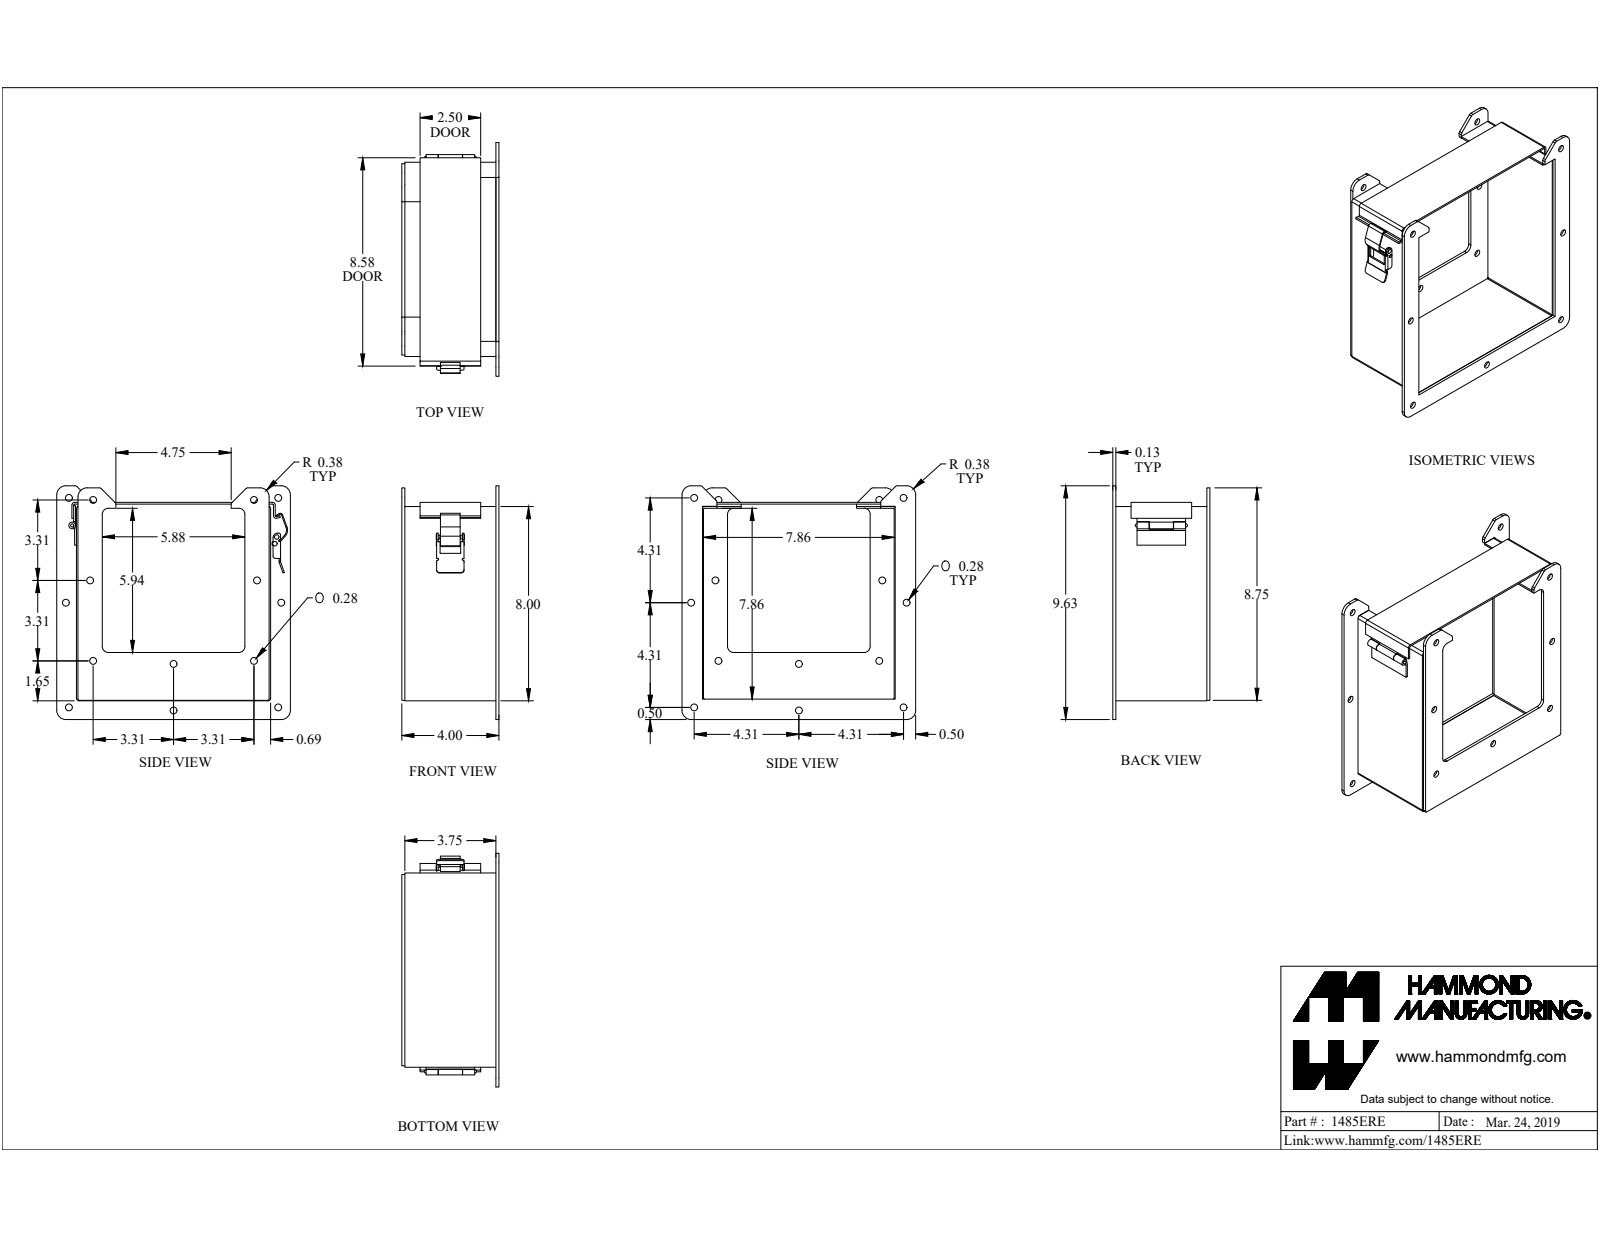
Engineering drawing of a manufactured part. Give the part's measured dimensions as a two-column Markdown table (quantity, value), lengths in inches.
| quantity | value |
| --- | --- |
| part name | 1485ERE |
| STEP written by | SolidWorks 2019 (CONFIG_CONTROL_DESIGN) |
| units | inches |
| bodies | 10 solids, 255 faces (146 planar, 107 cylindrical, 2 other) |
| overall size | 9.625 × 9.625 × 4 |
| volume | 15.79 in³ |
| surface area | 387 in² |
| round holes (diameter × count) | 0.281 × 14, 0.125 × 1, 0.13 × 1, 0.164 × 1 |
| round bosses / shafts (diameter × count) | 0.187 × 2, 0.275 × 1, 0.156 × 1, 0.125 × 1 |
| partial cylindrical surfaces (radius × count) | 0.125 × 11, 0.016 × 7, 0.036 × 7, 0.108 × 7, 0.375 × 6, 0.25 × 4, 0.035 × 3, 0.039 × 3 |
| main face-to-face distances | 0.072, 7.928, 8.1, 8, 7.856, 0.125, 3.875, 4, 3.875, 3.75 |
| hole center spacings | 3.315, 7.519, 4.315, 6.625, 9.755, 1.004, 1.356, 2.161 |
